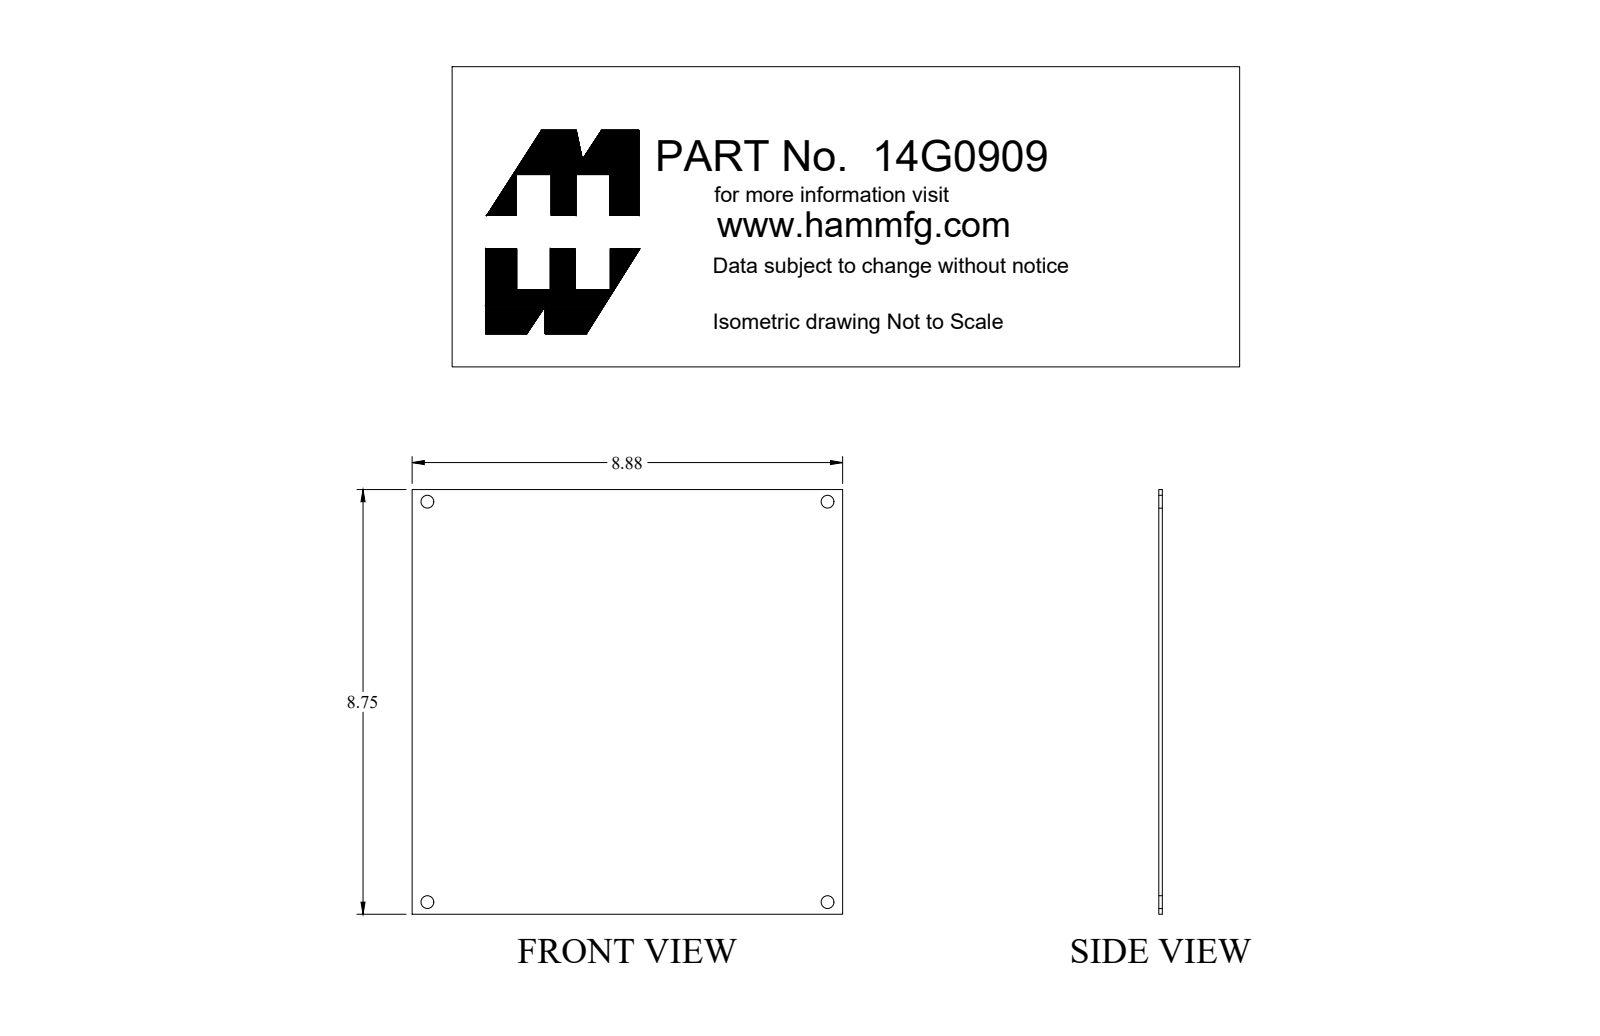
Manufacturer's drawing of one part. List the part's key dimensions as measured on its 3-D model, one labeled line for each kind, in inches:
Part name (STEP PRODUCT): 14G0909
STEP written by: SolidWorks 2018 (AUTOMOTIVE_DESIGN)
Units: inches
Bodies: 1 solid, 10 faces (6 planar, 4 cylindrical, 0 other)
Overall size (bounding box): 8.875 × 8.75 × 0.072
Volume: 5.575 in³ · Surface area: 157.6 in²
Round holes (diameter × count): ⌀0.265 ×4
Main face-to-face distances: 0.072, 8.75, 8.875
Hole centre spacings: 8.25, 11.667
